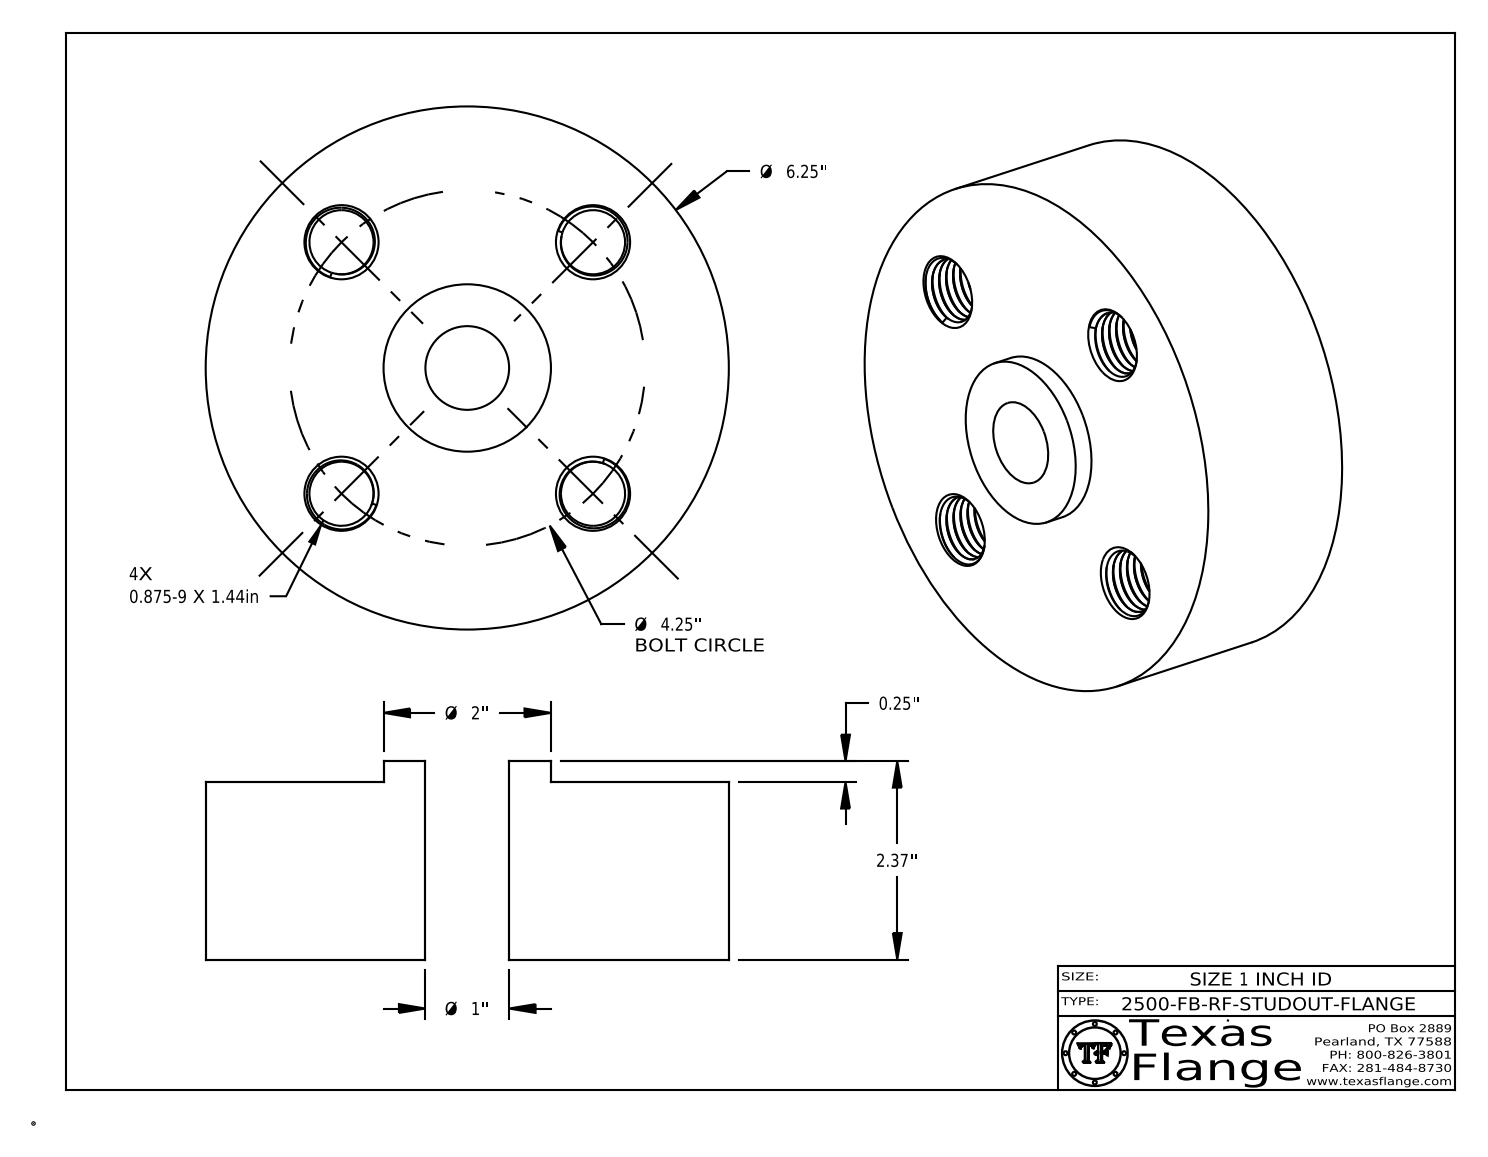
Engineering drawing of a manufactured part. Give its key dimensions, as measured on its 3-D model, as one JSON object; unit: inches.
{"part_name": "1-2500-FB-RF-STUDOUT-FLANGE", "step_written_by": "CATIA V5 STEP AP214 (AUTOMOTIVE_DESIGN)", "units": "inches", "bodies": {"solids": 1, "faces": 634, "planar": 368, "cylindrical": 106, "other": 160}, "overall_size": [6.25, 6.25, 2.37], "volume_in3": 60.91, "surface_area_in2": 128.8, "round_holes": [[0.766, 4], [1, 2]], "round_bosses_or_shafts": [[0.061, 8], [6.25, 1], [2, 1], [0.788, 1]], "face_to_face_distances": [2.12, 0.25, 2.37, 0.015, 2.355, 2.105, 0.298, 0.292, 0.054, 0.248], "hole_center_spacings": [2.125, 3.006, 1.626, 3.927, 4.25]}
